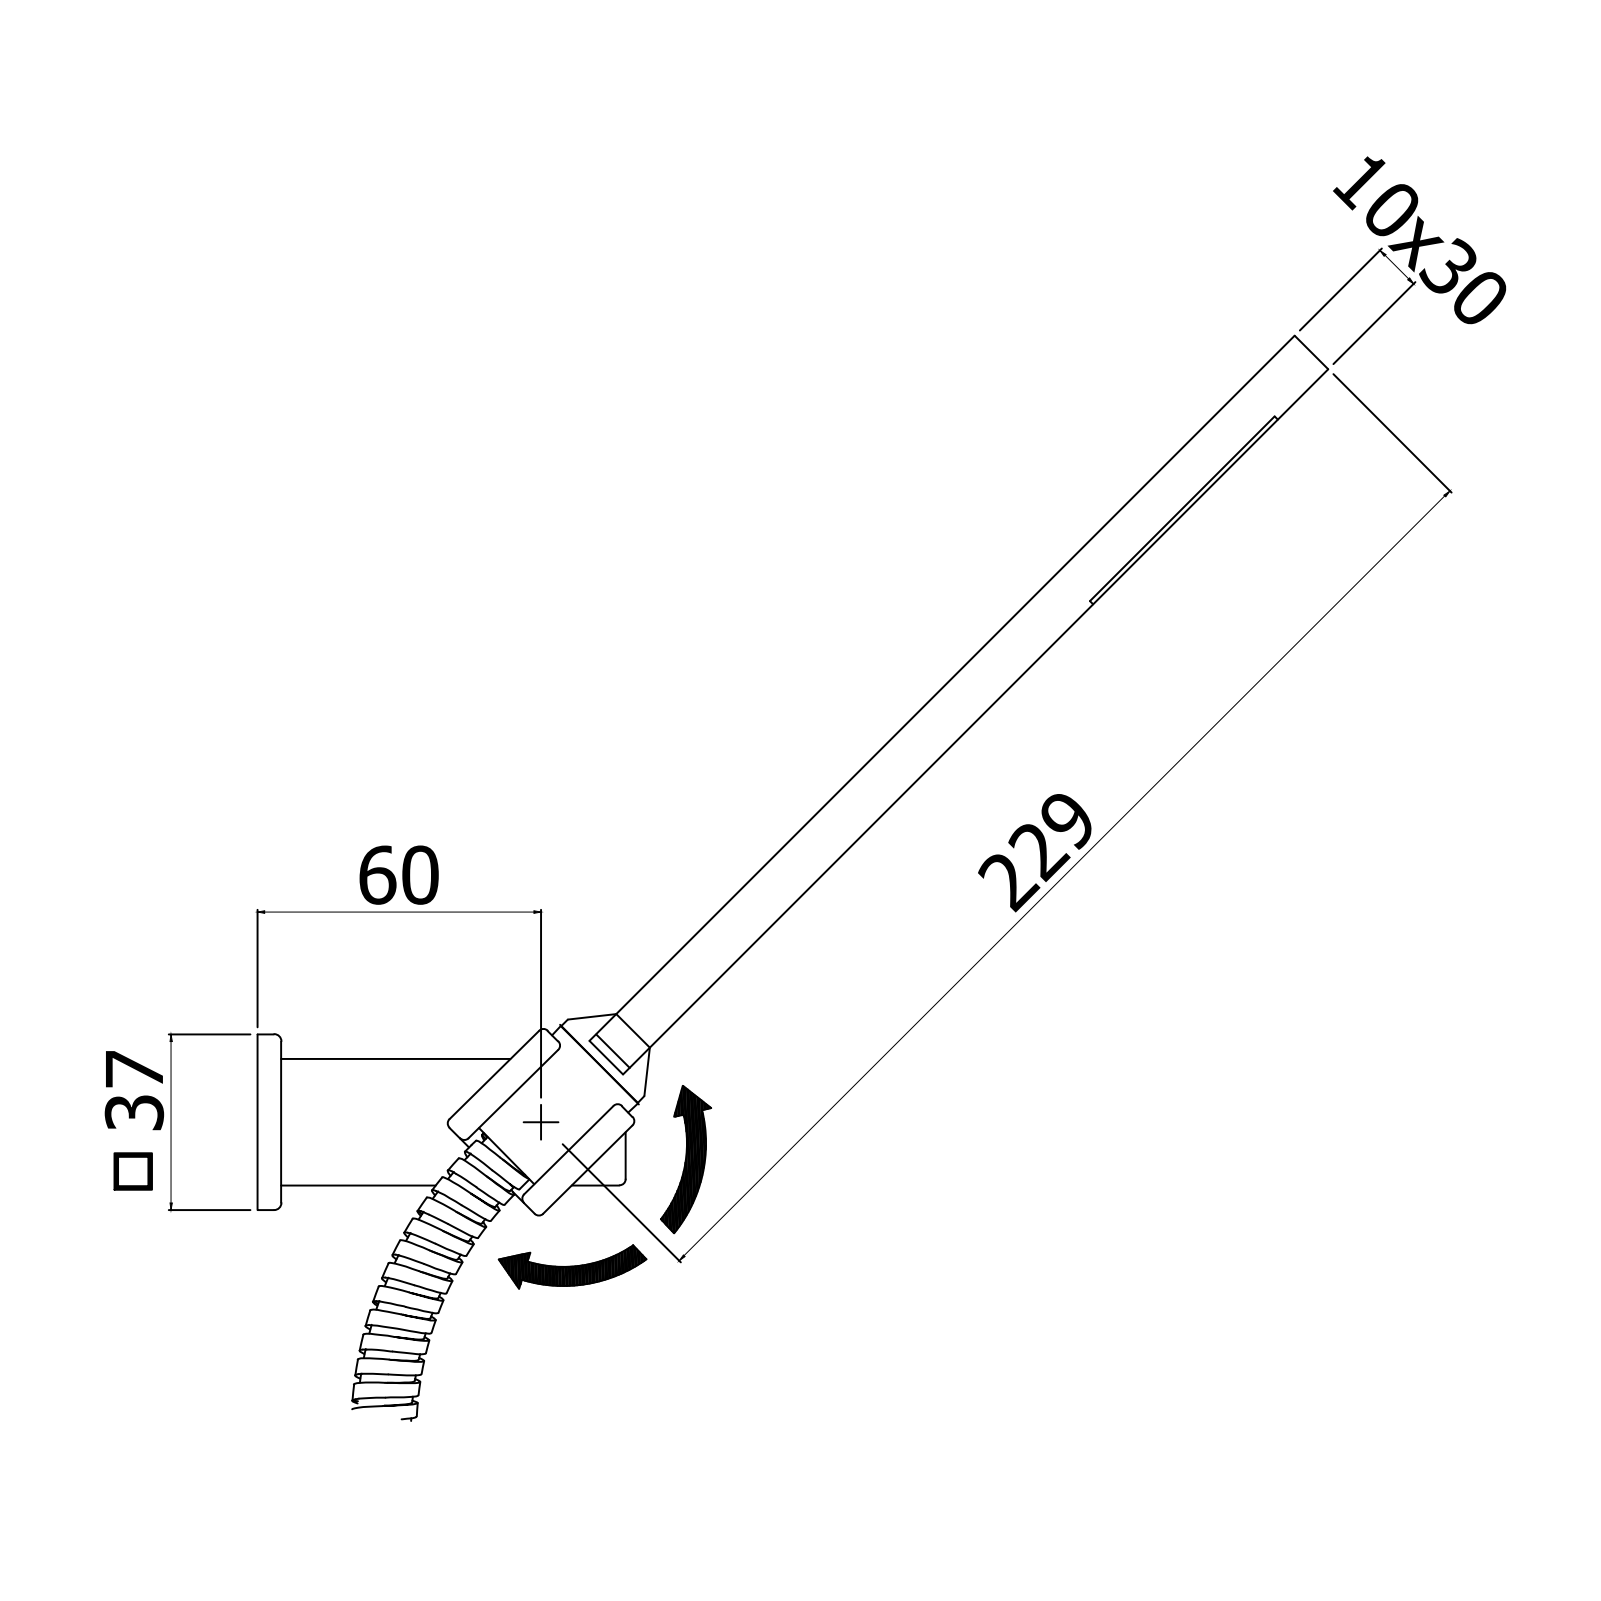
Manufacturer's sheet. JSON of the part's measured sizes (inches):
{"part_name": "ZDUP058CR", "step_written_by": "CREO PARAMETRIC BY PTC INC, 2020044 (CONFIG_CONTROL_DESIGN)", "units": "inches", "bodies": {"solids": 1, "faces": 420, "planar": 275, "cylindrical": 67, "other": 78}, "overall_size": [12.965, 4.62, 3.031], "volume_in3": 9.829, "surface_area_in2": 72.9, "round_bosses_or_shafts": [[0.079, 11], [0.886, 1]], "partial_cylinders_radius": [[0.039, 32], [0.02, 6], [0.157, 2], [4.449, 1]], "face_to_face_distances": [0.394, 1.083, 1.949, 1.181, 0.039, 3.13, 0.118, 0.866, 0.386, 2.047]}
